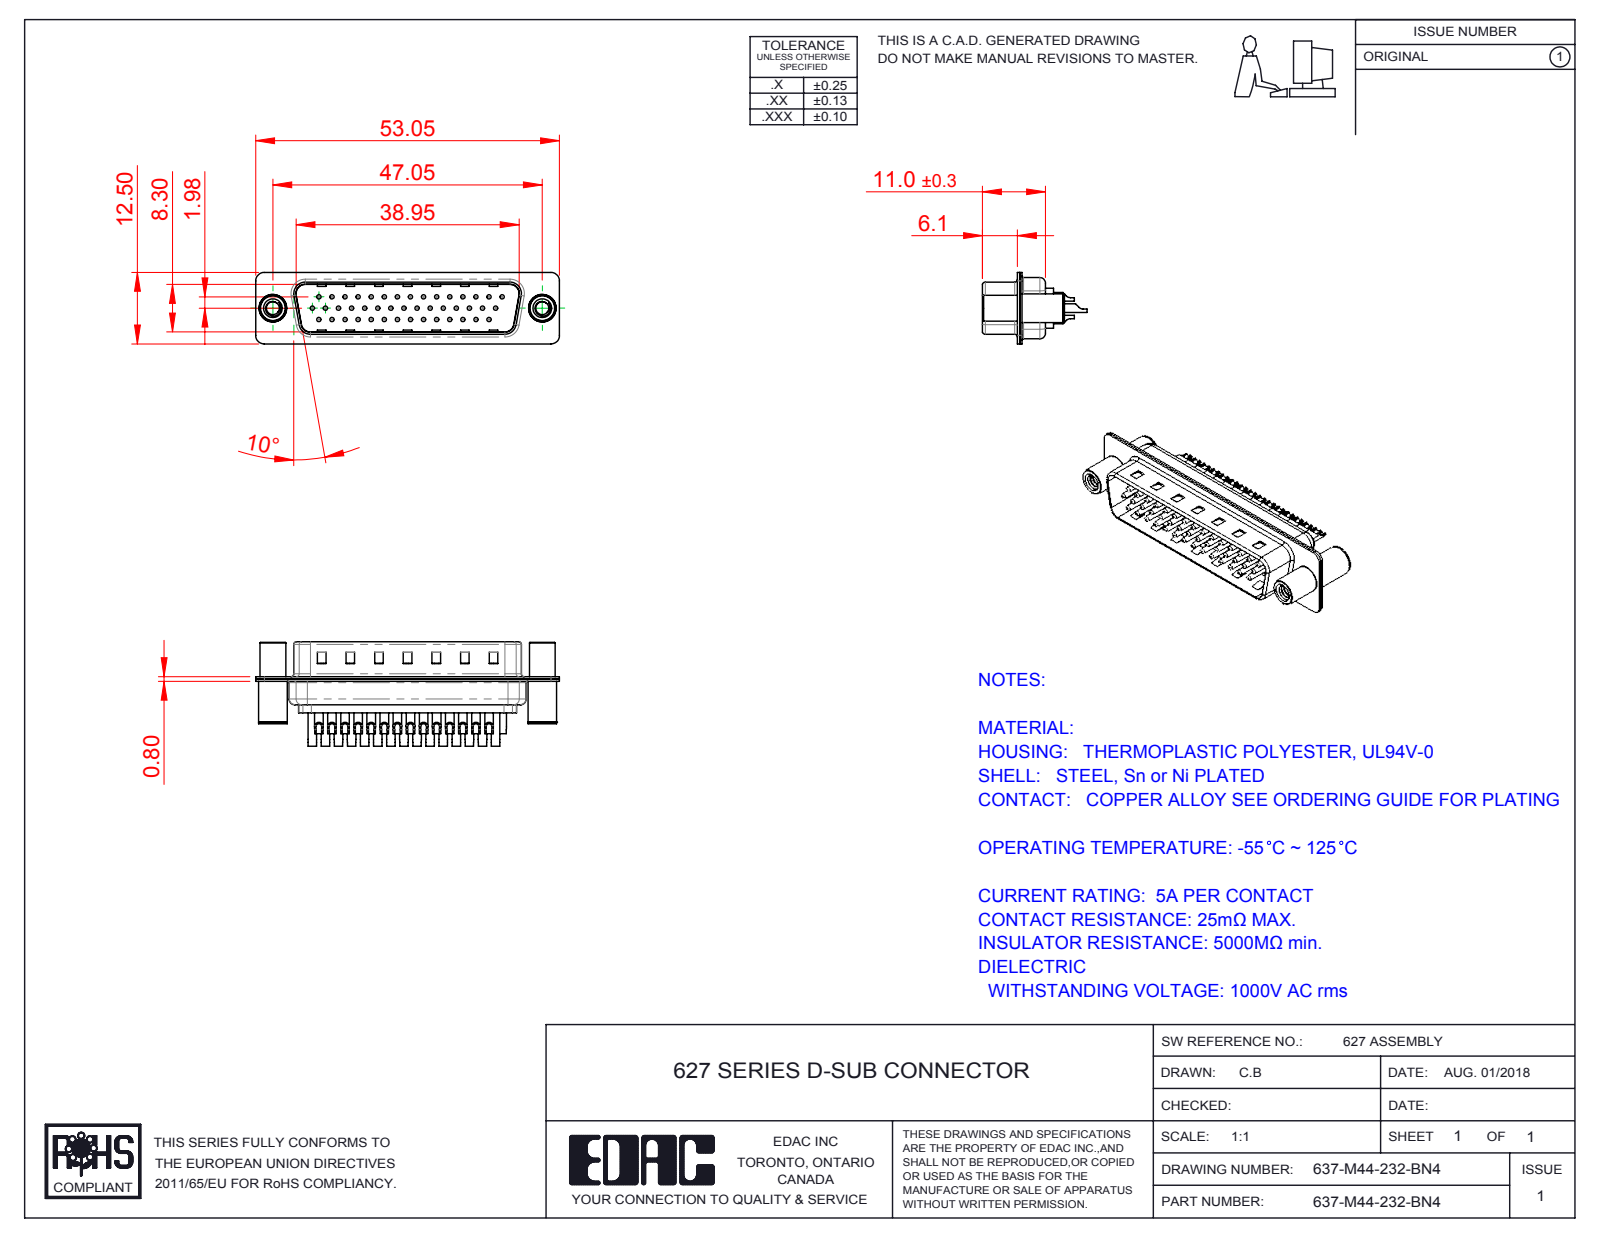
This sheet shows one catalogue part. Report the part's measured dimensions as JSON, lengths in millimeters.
{"part_name": "637M Shell Front_44 Contacts; 637M 4-40 Threaded Standoff and Board Spacer; 637M Shell Rear_44 Contacts; 637-M44-232-BN4 (+4 more)", "step_written_by": "SolidWorks 2016 (CONFIG_CONTROL_DESIGN)", "units": "millimeters", "bodies": {"solids": 49, "faces": 2090, "planar": 573, "cylindrical": 893, "other": 624}, "overall_size": [53.05, 18.25, 12.5], "volume_mm3": 3261, "surface_area_mm2": 9539, "round_holes": [[0.75, 44], [1, 44], [1.6, 44], [2, 44], [2.26, 2], [3.26, 2], [4, 2], [4.8, 2]], "round_bosses_or_shafts": [[1.5, 44], [2, 3], [0.75, 3], [5, 2], [4.9, 2], [4.5, 2]], "partial_cylinders_radius": [[1.5, 16], [2, 12], [0.5, 8], [1.6, 8], [1, 7], [0.25, 4], [0.6, 4], [0.65, 4]], "face_to_face_distances": [0.4, 0.8, 9.5, 9.1, 8.7, 9.9, 0.75, 0.35, 1.1, 1.2], "hole_center_spacings": [2.28, 3.96, 2.29, 4.57, 8.24, 6.86, 11.43, 14.99]}
